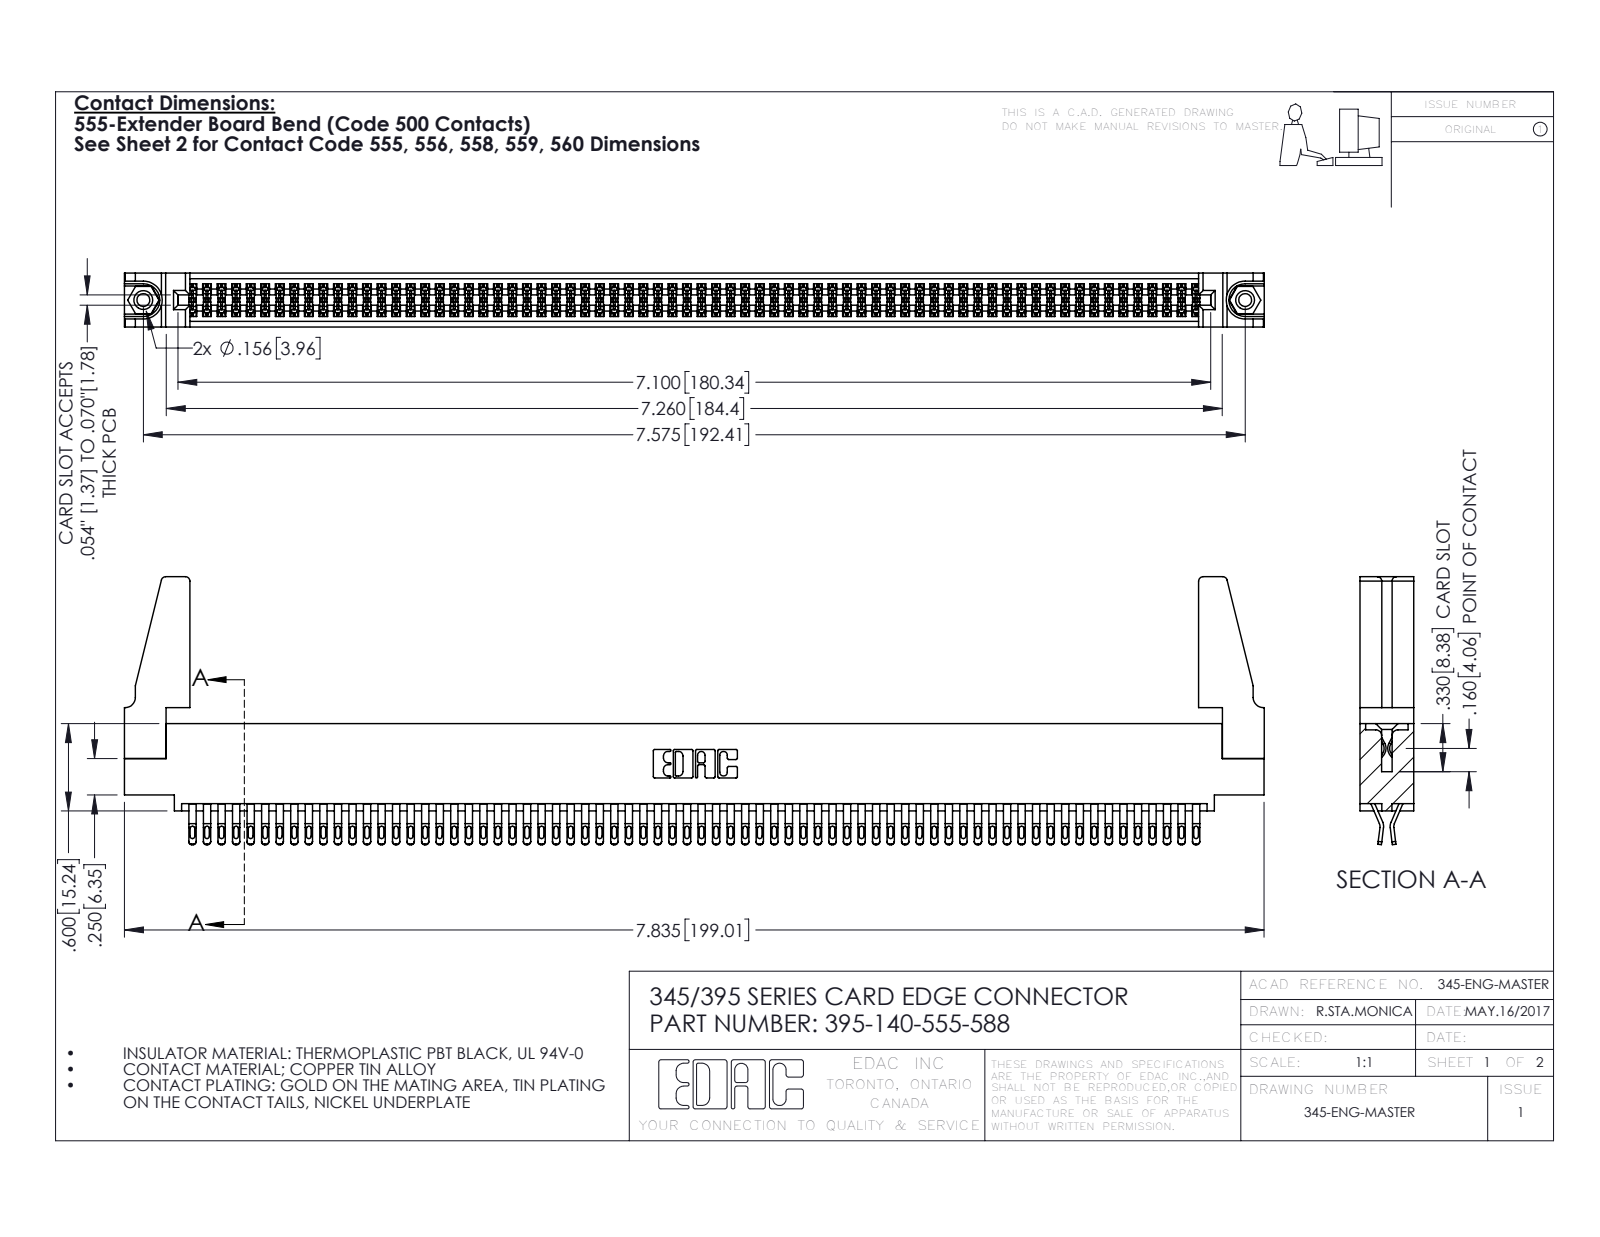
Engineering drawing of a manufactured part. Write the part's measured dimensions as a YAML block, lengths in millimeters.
part_name: "395-140-555-588; 345-250-001_345-250-001-102; 345-292-001_555 Tail; 345-220-078_345-220-088 (+1 more)"
step_written_by: "SolidWorks 2016 (CONFIG_CONTROL_DESIGN)"
units: millimeters
bodies: {solids: 145, faces: 8094, planar: 4496, cylindrical: 3582, other: 16}
overall_size: [199, 46.8, 9.4]
volume: 23170
surface_area: 34630
round_holes:
  - {diameter: 2.3, count: 2}
  - {diameter: 3.2, count: 2}
  - {diameter: 4, count: 2}
  - {diameter: 1.6, count: 1}
round_bosses_or_shafts:
  - {diameter: 3.9, count: 2}
partial_cylinders:
  - {radius: 0.4, count: 350}
  - {radius: 0.5, count: 280}
  - {radius: 0.2, count: 210}
  - {radius: 0.3, count: 22}
  - {radius: 0.8, count: 8}
  - {radius: 0.2, count: 6}
  - {radius: 0.8, count: 6}
  - {radius: 0.7, count: 3}
face_to_face_distances: [1.8, 7.6, 9.4, 0.6, 5.1, 2.5, 6.9, 5.7, 4.4, 3.8]
hole_center_spacings: [6.9, 186.4, 192.4]
